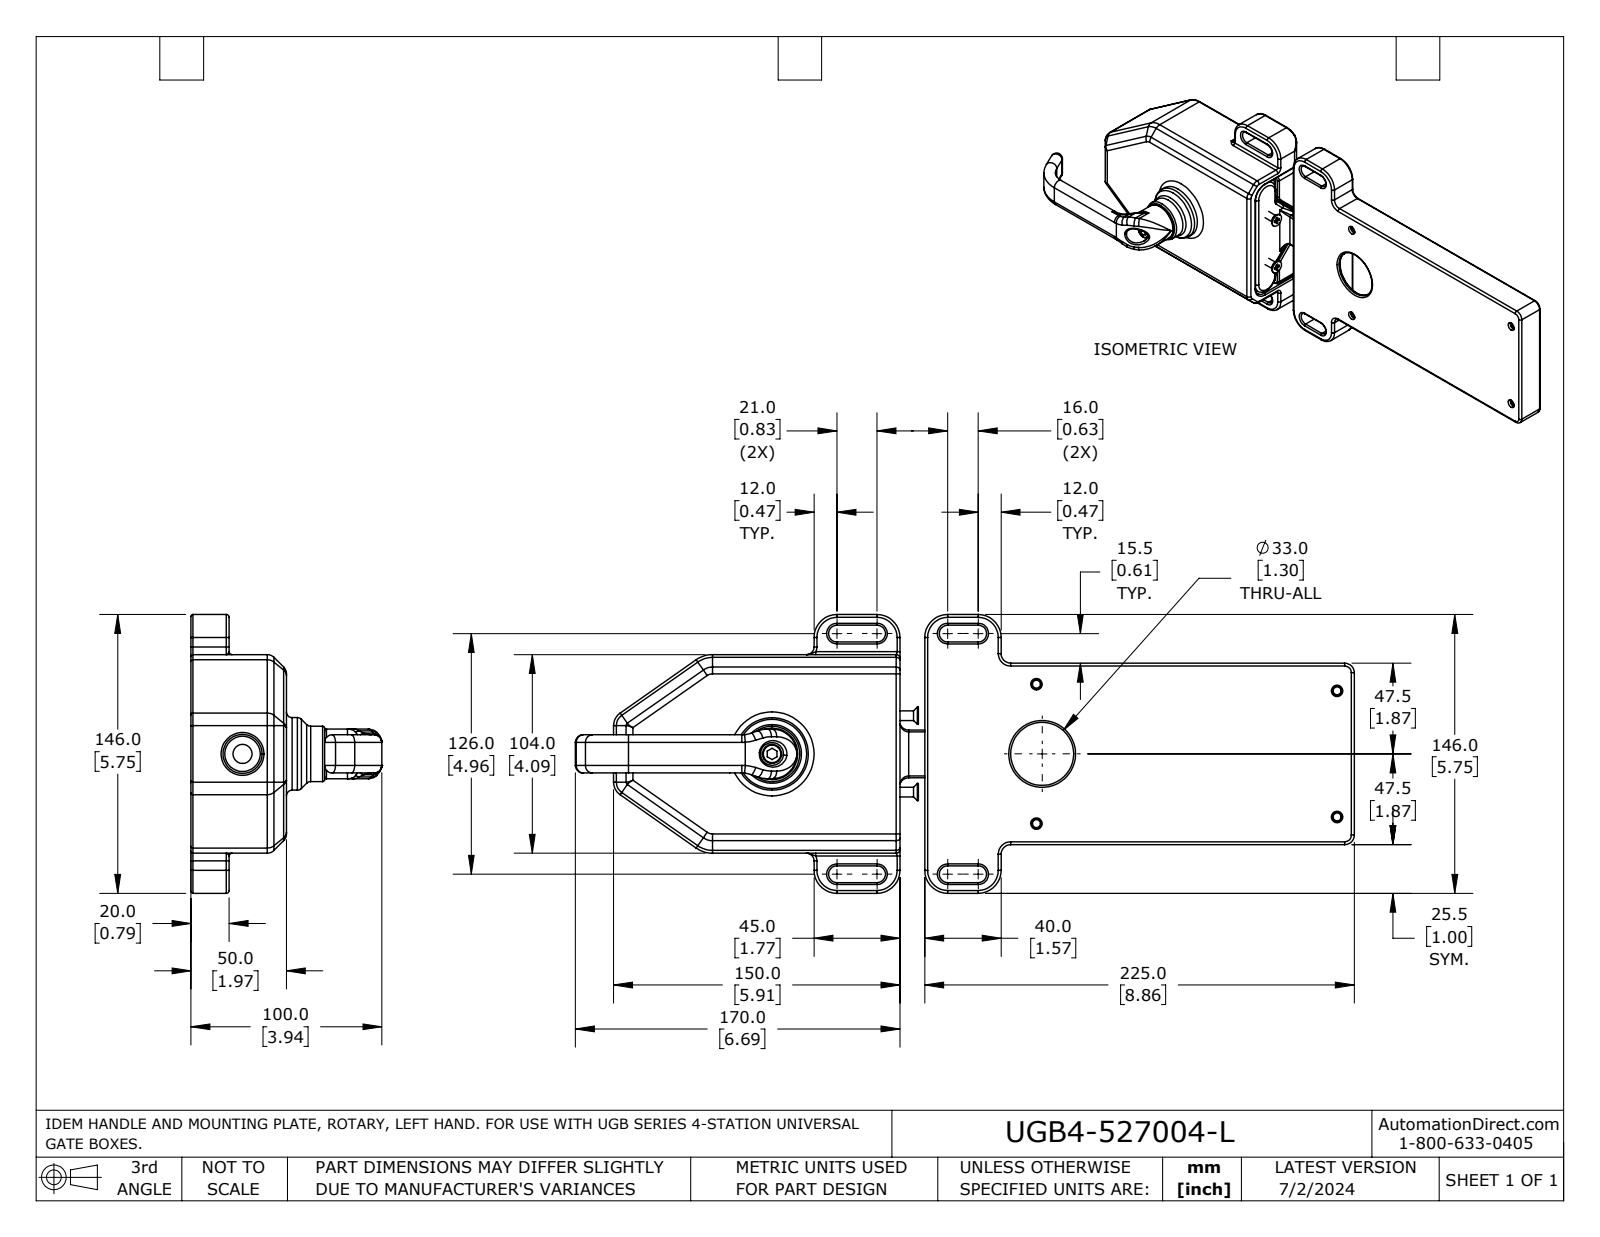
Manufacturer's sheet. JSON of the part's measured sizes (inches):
{"part_name": "UGB4-527004 -L", "step_written_by": "SolidWorks 2023 (AUTOMOTIVE_DESIGN)", "units": "inches", "bodies": {"solids": 14, "faces": 1766, "planar": 434, "cylindrical": 688, "other": 644}, "overall_size": [16.063, 5.748, 3.937], "volume_in3": 26.85, "surface_area_in2": 347, "round_holes": [[0.165, 10], [0.217, 4], [0.236, 4], [0.13, 2], [0.413, 2], [0.157, 1], [0.248, 1], [0.26, 1], [0.268, 1], [0.472, 1], [0.559, 1], [0.827, 1]], "round_bosses_or_shafts": [[0.335, 4], [0.197, 4], [0.173, 4], [0.787, 2], [0.354, 2], [0.315, 2], [0.276, 2], [0.236, 2]], "partial_cylinders_radius": [[0.039, 269], [0.079, 91], [0.197, 28], [0.118, 24], [0.02, 20], [0.031, 19], [0.157, 12], [0.059, 11]], "face_to_face_distances": [0.098, 0.65, 0.138, 0.039, 0.748, 1.831, 1.929, 0.551, 1.693, 1.28], "hole_center_spacings": [0.812, 1.442, 1.562, 2.195, 2.665, 3.295, 3.645, 3.744]}
